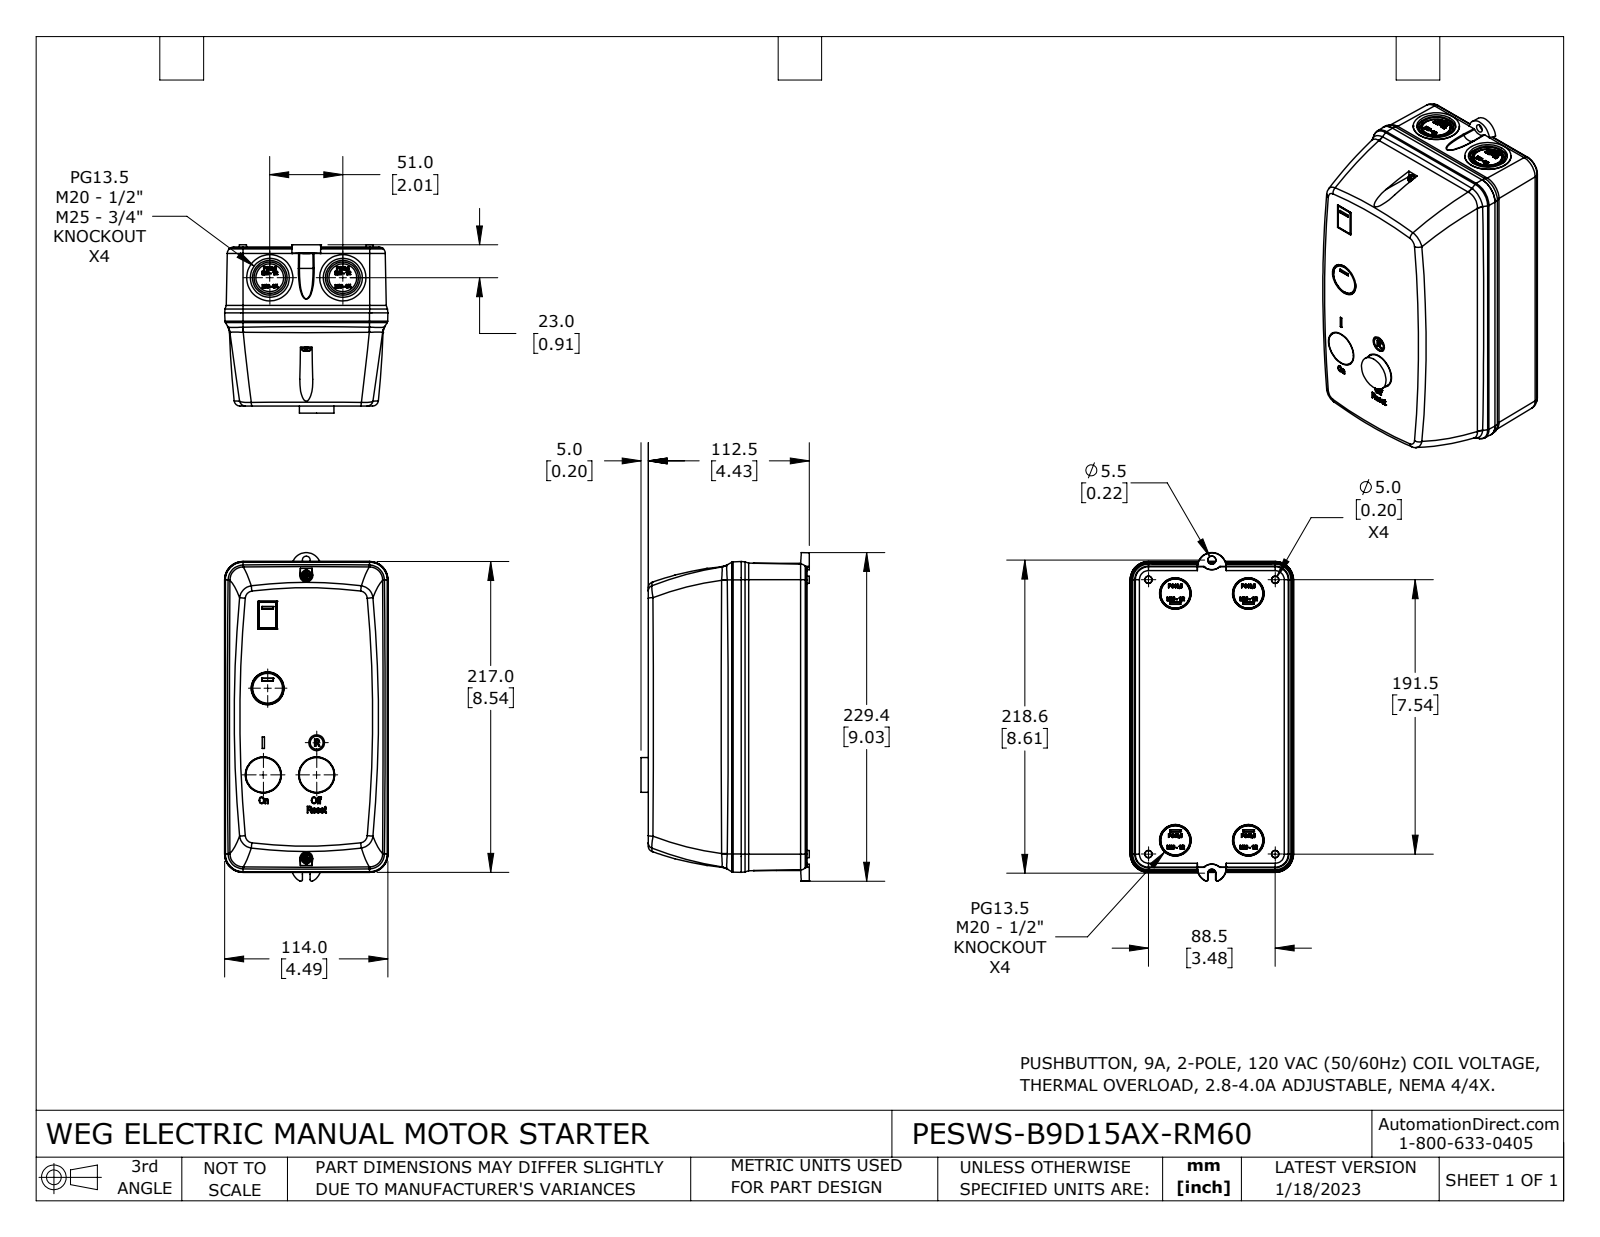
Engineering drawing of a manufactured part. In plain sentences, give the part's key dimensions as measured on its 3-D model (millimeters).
The part is named "PESWS-B9D15AX-RM60". Its 3-D file was written by "SolidWorks 2021 (CONFIG_CONTROL_DESIGN)". It is 6 solids with 2195 faces: 1110 planar, 92 cylindrical and 993 other. Overall it measures 229.44 by 117.5 by 114.01 millimeters. Its volume is 2 457 000 cubic millimeters and its surface area 166 196 square millimeters. Round holes: 2 of diameter 4.4, 2 of diameter 21.91, 2 of diameter 27.24, 1 of diameter 5.5, 1 of diameter 11. Round bosses or shafts: 2 of diameter 32.26, 2 of diameter 24.25, 2 of diameter 24.2, 2 of diameter 19.37, 2 of diameter 7, 2 of diameter 3, 1 of diameter 9. Partial cylindrical surfaces (rounded edges, fillets, slot ends): 4 of radius 2, 4 of radius 4.61, 4 of radius 9.54, 2 of radius 6.54, 2 of radius 7.54, 1 of radius 2.08, 1 of radius 2.17, 1 of radius 2.75. The main face-to-face distances are 46, 65, 111, 0.5, 110.5, 45.5, 110, 1, 109.5, 64. The hole center spacings are 10.5, 51, 81.32, 117.22, 127.71, 198, 208.5.
